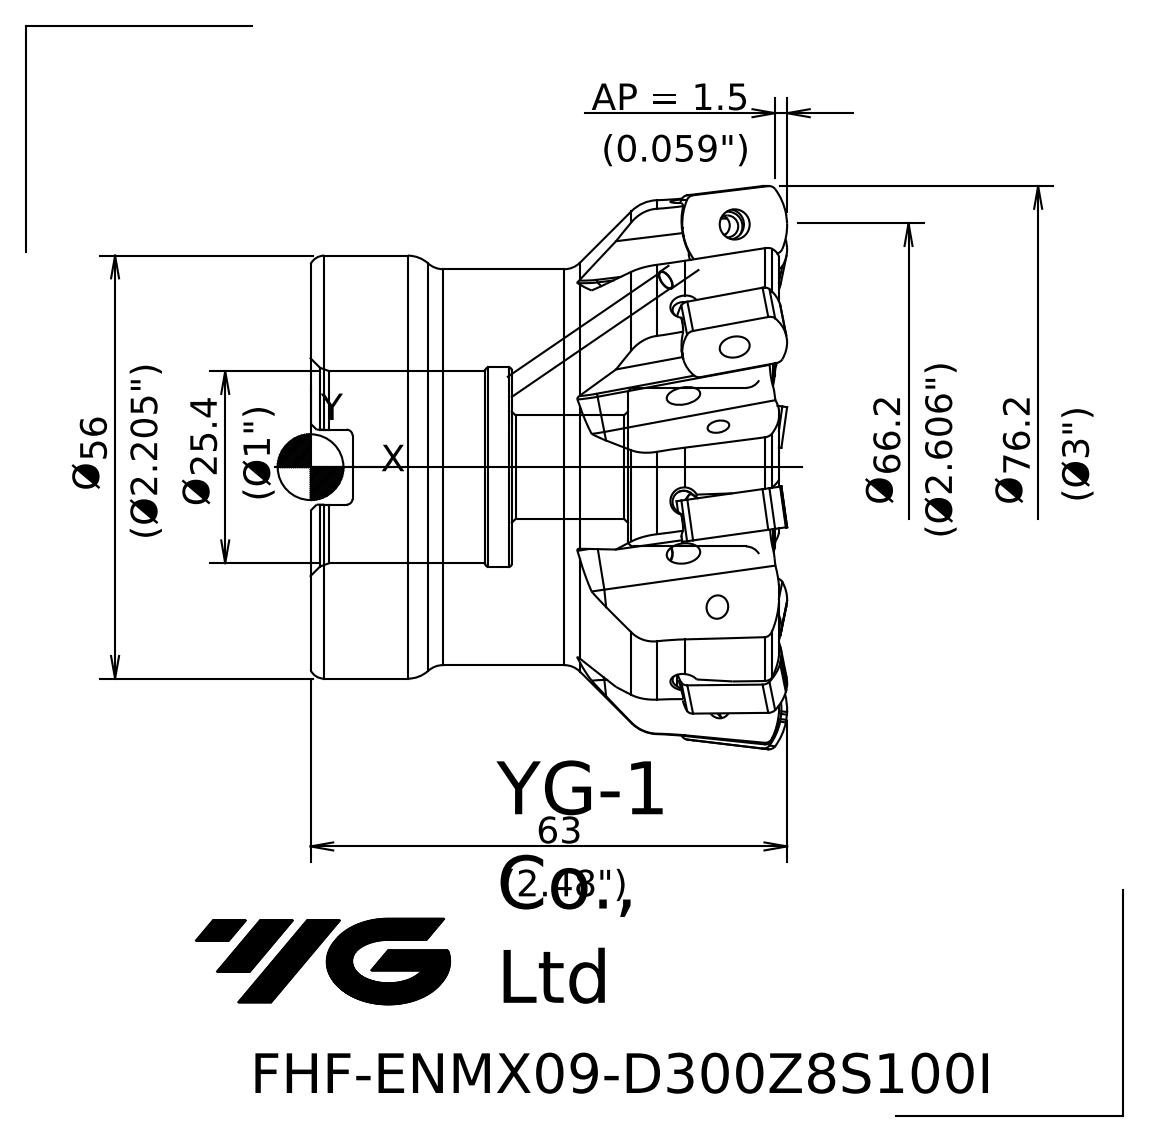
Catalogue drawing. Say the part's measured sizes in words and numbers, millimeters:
The part is named "120185C07CB1h848". Its 3-D file was written by "SIEMENS PLM Software NX 10.0 (AP203_CONFIGURATION_CONTROLLED_3D_DESIGN_OF_MECHANICAL_PARTS_AND_ASSEMBLIES_MIM_LF)". It is 1 solid with 70 faces: 17 planar, 10 cylindrical and 43 other. Overall it measures 76.21 by 76.21 by 63.02 millimeters. Its volume is 161 838 cubic millimeters and its surface area 23 559 square millimeters. Round holes: 1 of diameter 13.7, 1 of diameter 21, 1 of diameter 25.4, 1 of diameter 26.4. Round bosses or shafts: 1 of diameter 56, 1 of diameter 52.4. Partial cylindrical surfaces (rounded edges, fillets, slot ends): 2 of radius 0.8. The main face-to-face distances are 61.22, 12.06, 49.16, 37.22, 25.16, 24, 55.66, 43.6, 18.44, 5.56.
